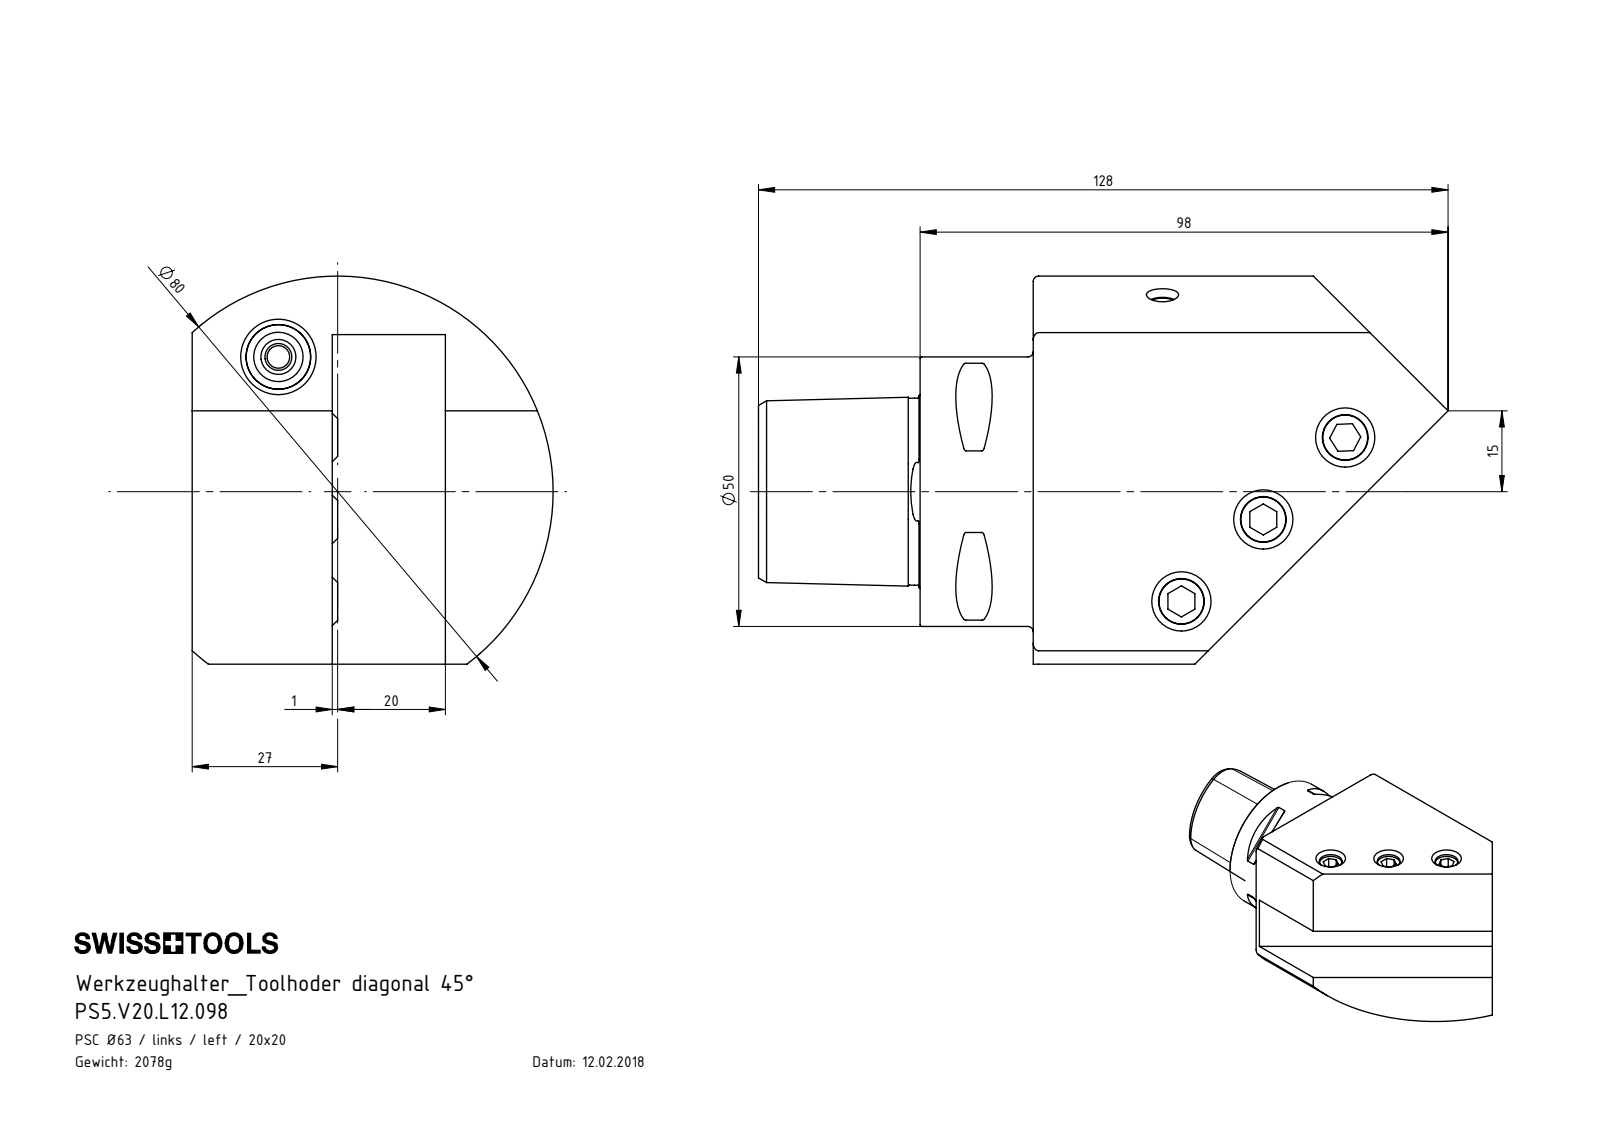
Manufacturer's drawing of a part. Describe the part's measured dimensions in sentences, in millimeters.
The part is named "KU1-U12.001.010_2; PS5-V20.L12.098_A; PS5.V20.L12.098; KVT_MB_600_060 (+3 more)". Its 3-D file was written by "SolidWorks 2017 (AUTOMOTIVE_DESIGN)". It is 8 solids with 176 faces: 61 planar, 37 cylindrical and 78 other. Overall it measures 128 by 72 by 67 millimeters. Its volume is 264 998 cubic millimeters and its surface area 42 429 square millimeters. Round holes: 3 of diameter 5, 3 of diameter 8.5, 1 of diameter 4, 1 of diameter 4.2, 1 of diameter 6, 1 of diameter 6.1, 1 of diameter 7, 1 of diameter 8.4, 1 of diameter 12, 1 of diameter 14, 1 of diameter 14.5, 1 of diameter 21. Round bosses or shafts: 3 of diameter 10, 1 of diameter 50, 1 of diameter 6. Partial cylindrical surfaces (rounded edges, fillets, slot ends): 8 of radius 0.5, 1 of radius 4, 1 of radius 40. The main face-to-face distances are 21, 20, 47, 26, 51, 30, 19.18, 102, 72, 8. The hole center spacings are 21.5, 21.51, 26, 27.31, 41.79, 43.01, 51.97, 65.73.
